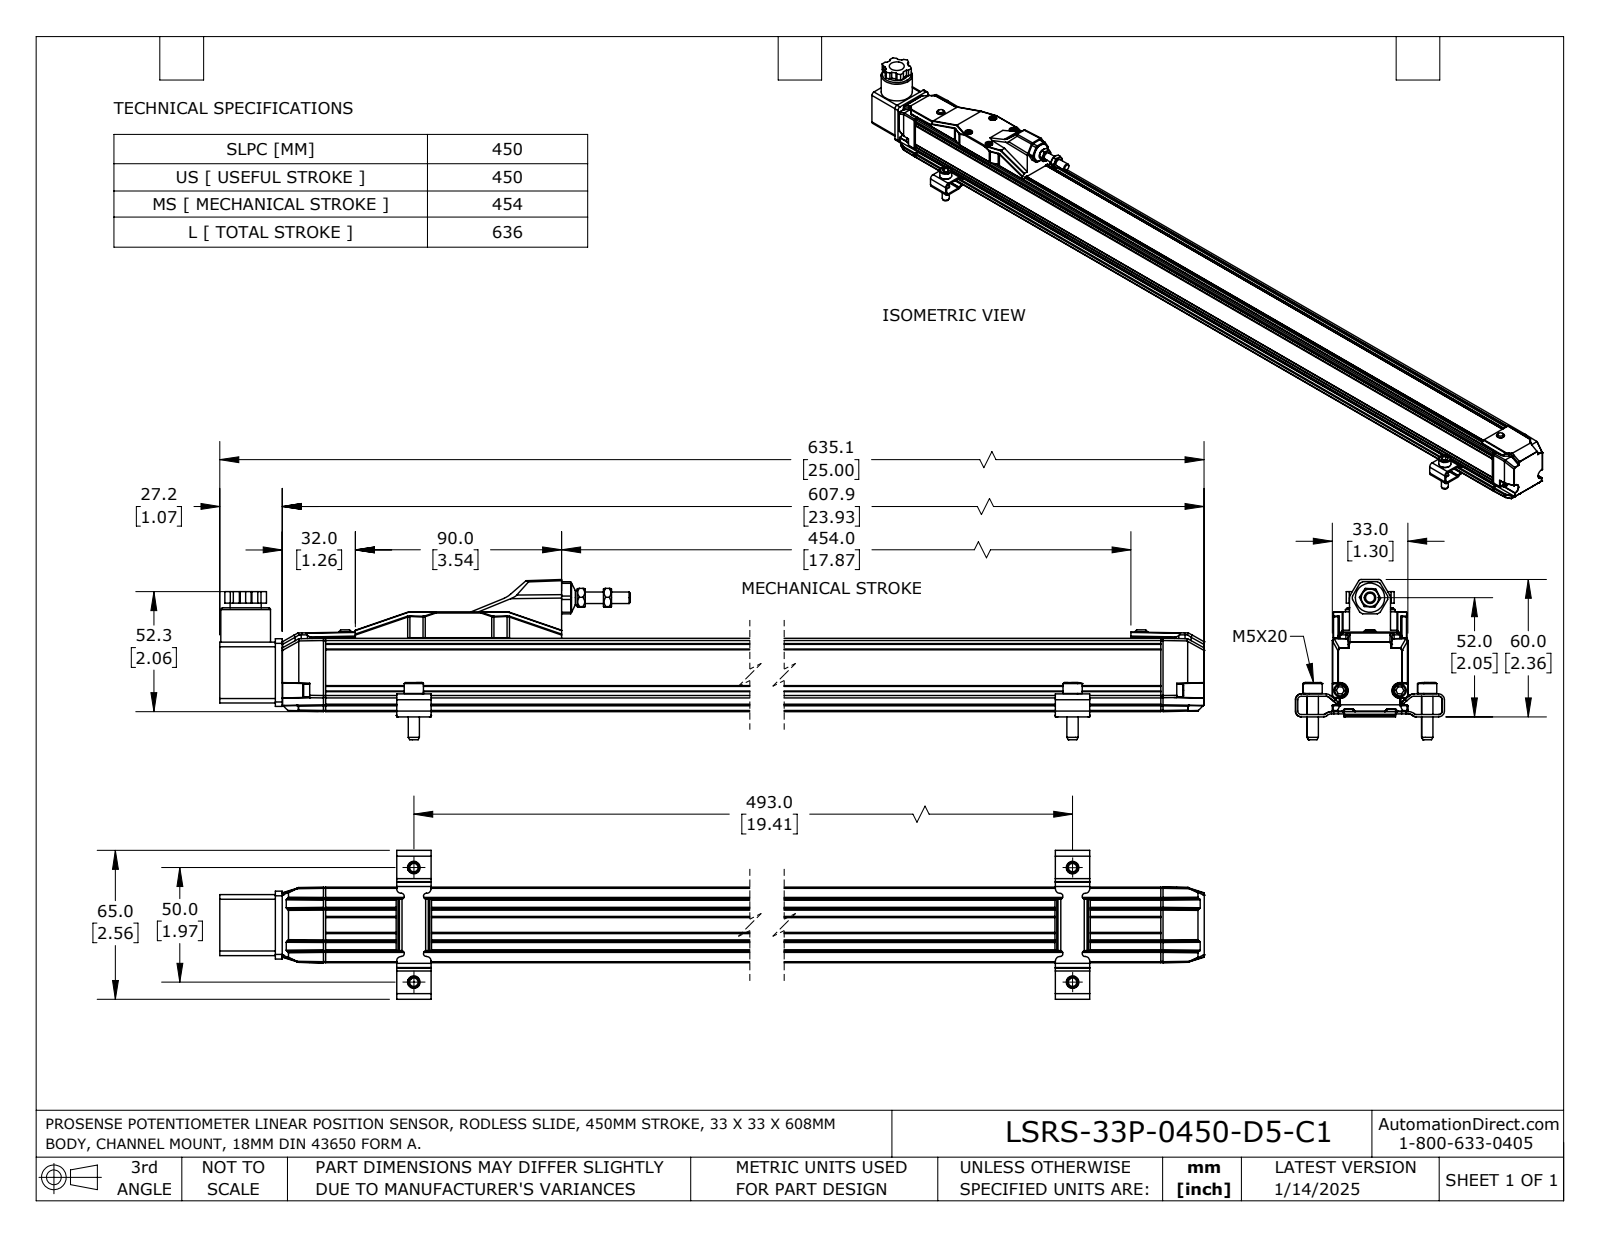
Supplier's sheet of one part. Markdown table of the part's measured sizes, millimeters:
| quantity | value |
| --- | --- |
| part name | LSRS-33P-0450-D5-C1 |
| STEP written by | SolidWorks 2024 (AUTOMOTIVE_DESIGN) |
| units | millimeters |
| bodies | 11 solids, 1336 faces (841 planar, 363 cylindrical, 132 other) |
| overall size | 635.2 × 70 × 65 |
| volume | 610 900 mm³ |
| surface area | 154 300 mm² |
| round holes (diameter × count) | 4.7 × 4, 5.5 × 4, 2.7 × 2, 3.3 × 2, 2.8 × 1, 4 × 1, 5 × 1, 5.3 × 1, 5.9 × 1, 6 × 1, 7 × 1, 10 × 1 |
| round bosses / shafts (diameter × count) | 8.4 × 4, 4.9 × 4, 4.6 × 4, 5.6 × 2, 5.5 × 2, 3 × 2, 2.9 × 2, 2.9 × 2 |
| partial cylindrical surfaces (radius × count) | 0.5 × 82, 0.2 × 62, 2 × 44, 3 × 26, 1 × 10, 1.3 × 8, 1.5 × 8, 4 × 8 |
| main face-to-face distances | 33, 31.6, 3, 29.6, 6, 25.6, 0.9, 0.4, 32.6, 11.3 |
| hole center spacings | 15.2, 20, 23.7, 31, 32.7, 42.5, 50, 463.7 |
